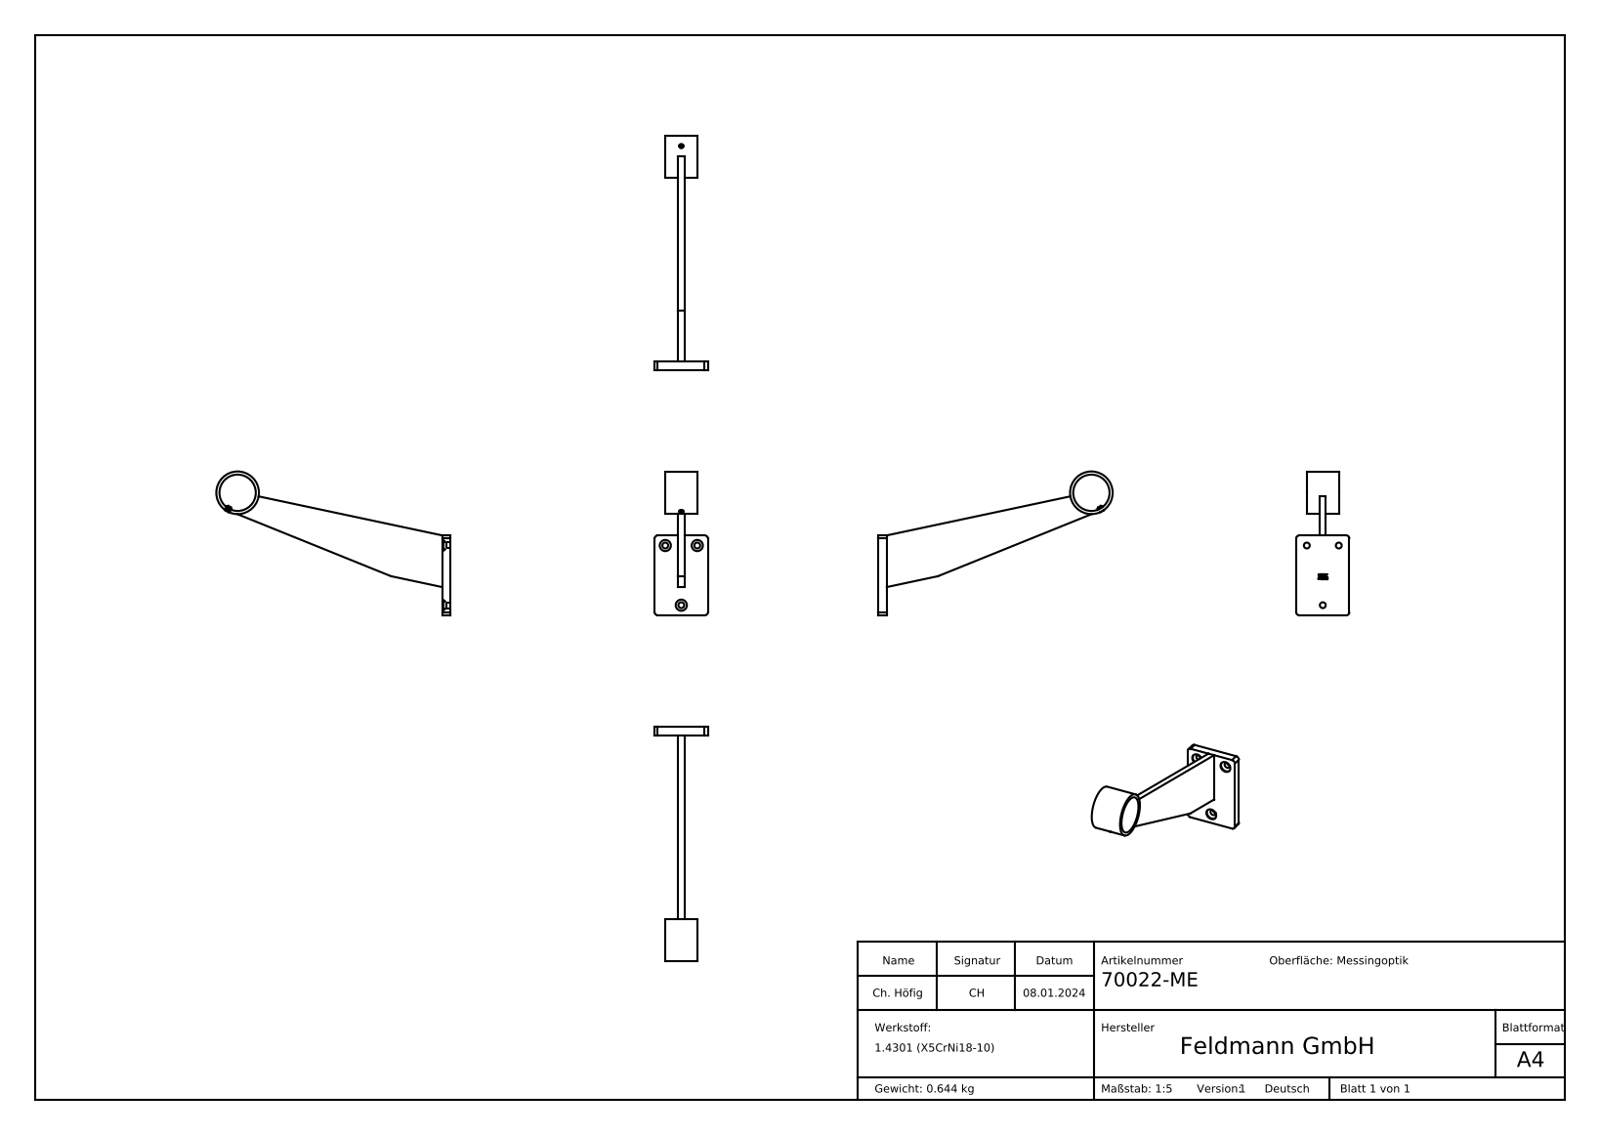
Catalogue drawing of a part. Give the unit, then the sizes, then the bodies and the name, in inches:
Units: inches
Overall size (bounding box): 8.661 × 5.315 × 1.969
Round holes (diameter × count): ⌀0.217 ×3, ⌀0.413 ×3, ⌀0.165 ×1, ⌀1.343 ×1
Round bosses / shafts (diameter × count): ⌀1.575 ×1, ⌀0.197 ×1
Partial cylindrical surfaces — rounded edges, fillets, slot ends (radius × count): R0.118 ×4
Main face-to-face distances: 0.236, 0.315, 0.866, 1.102, 0.394, 1.575, 0.472, 0.709, 1.969, 2.953
Hole centre spacings: 2.282, 1.181
Volume: 4.975 in³ · Surface area: 51.82 in²
Bodies: 2 solids, 247 faces (149 planar, 14 cylindrical, 84 other)
Part name (STEP PRODUCT): 70022-ME Teil1; 70022-ME; DIN913_DIN 913 M5x5
STEP written by: SolidWorks 2018 (CONFIG_CONTROL_DESIGN)
